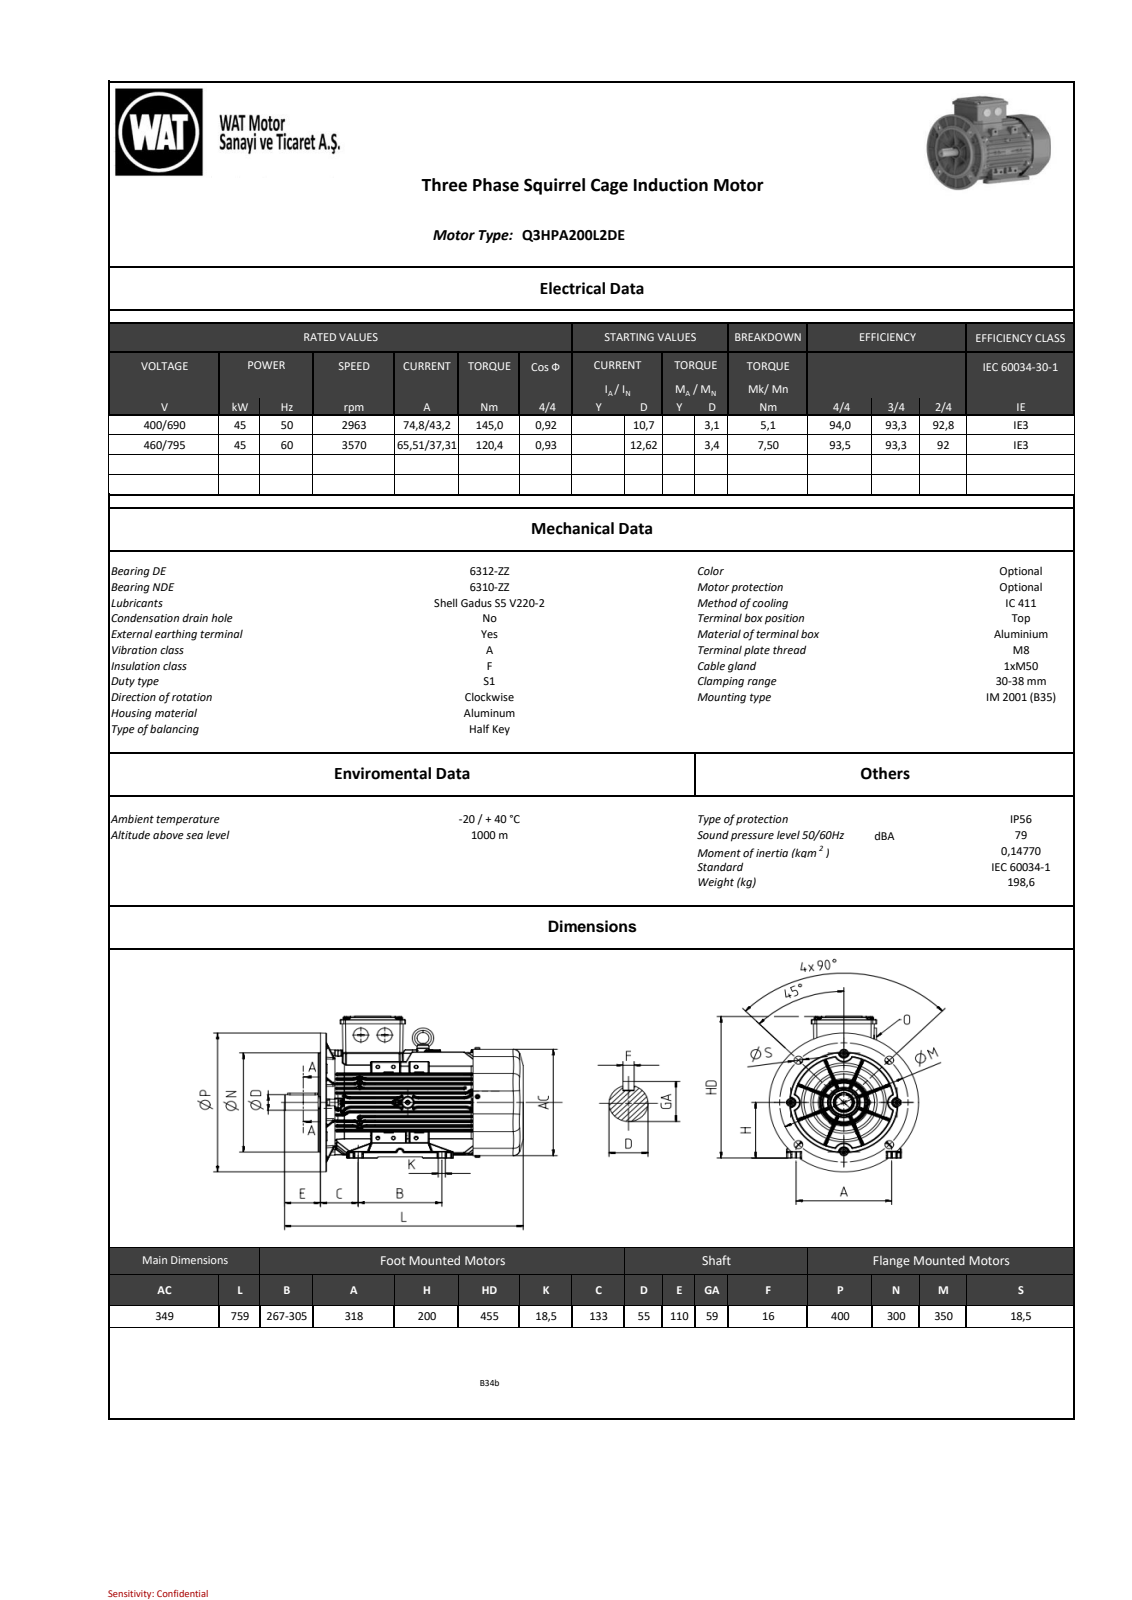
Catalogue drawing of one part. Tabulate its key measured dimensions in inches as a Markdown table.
| quantity | value |
| --- | --- |
| part name | model1_objects |
| STEP written by | SIEMENS PLM Software NX2206.8101 (AUTOMOTIVE_DESIGN) |
| units | inches |
| bodies | 0 solids, 14591 faces (3654 planar, 4776 cylindrical, 6161 other) |
| overall size | 29.882 × 17.795 × 15.736 |
| round holes (diameter × count) | 0.22 × 8, 0.169 × 4, 0.256 × 4, 0.354 × 4, 0.728 × 4, 0.157 × 3, 0.217 × 3, 0.33 × 2, 0.372 × 2, 0.866 × 2, 0.986 × 2, 1.905 × 2 |
| round bosses / shafts (diameter × count) | 0.512 × 4, 0.394 × 4, 0.315 × 4, 2.165 × 3, 1.969 × 3, 2.016 × 2, 1.896 × 2, 0.984 × 2 |
| partial cylindrical surfaces (radius × count) | 0.02 × 1659, 0.039 × 784, 0.079 × 760, 0.197 × 123, 0.004 × 122, 0.157 × 72, 0.118 × 61, 0.394 × 26 |
| main face-to-face distances | 0.236, 0.047, 0.638, 1.279, 0.641, 0.118, 22.559, 6.734, 6.844, 5.565 |
| hole center spacings | 5.088, 12.223, 5.354, 3.077, 6.691, 6.142, 6.339, 6.889 |
